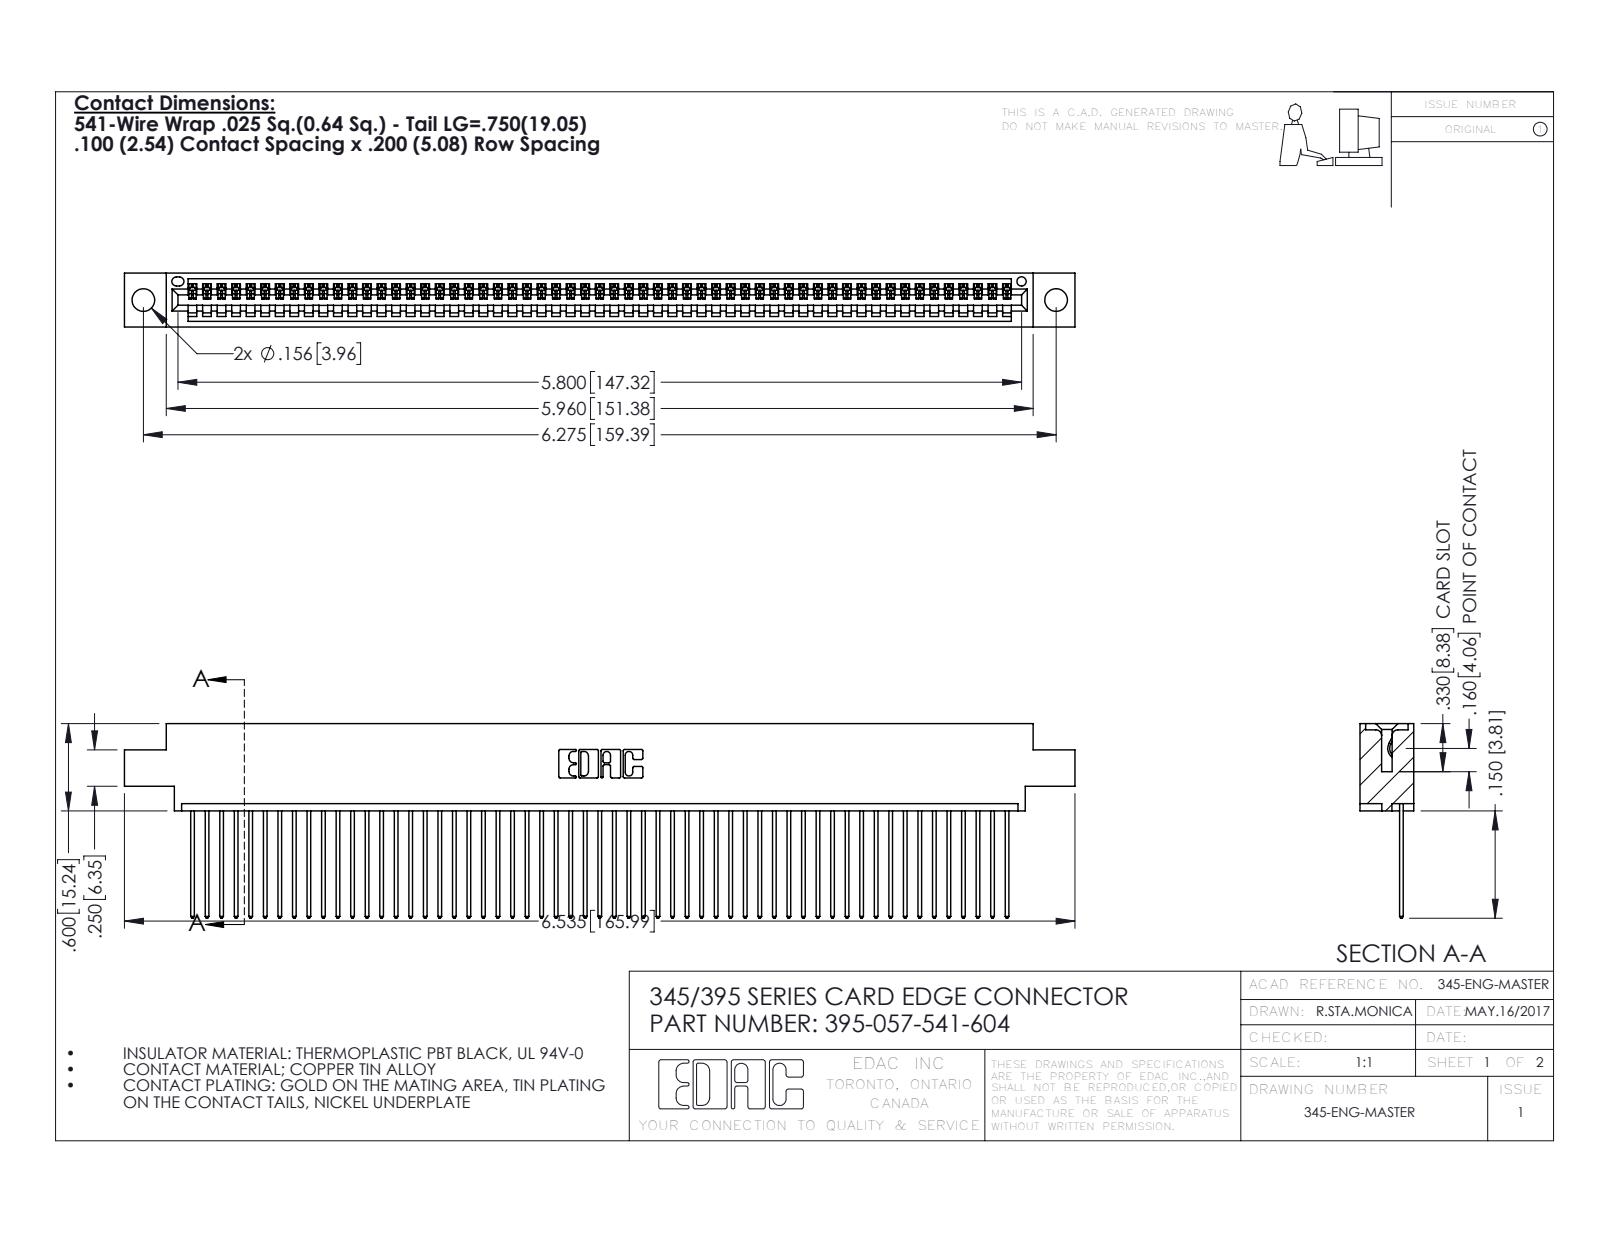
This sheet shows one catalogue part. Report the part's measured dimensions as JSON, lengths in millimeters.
{"part_name": "345-292-001_345-293-141; 395-057-541-604; 345 Part_0.170 Offset - 0.156 Dia-TH", "step_written_by": "SolidWorks 2016 (CONFIG_CONTROL_DESIGN)", "units": "millimeters", "bodies": {"solids": 58, "faces": 3436, "planar": 2364, "cylindrical": 1072, "other": 0}, "overall_size": [166, 34, 9.4], "volume_mm3": 15900, "surface_area_mm2": 22340, "round_holes": [[4, 2], [1.6, 1]], "partial_cylinders_radius": [[0.2, 114], [0.3, 114], [0.3, 22], [0.2, 6], [0.8, 6], [0.7, 3], [0.8, 2], [1, 2]], "face_to_face_distances": [1.8, 7.6, 2.5, 6.9, 0.6, 9.4, 5.1, 5.7, 4.4, 3.8], "hole_center_spacings": [6.9, 153.4, 159.4]}
